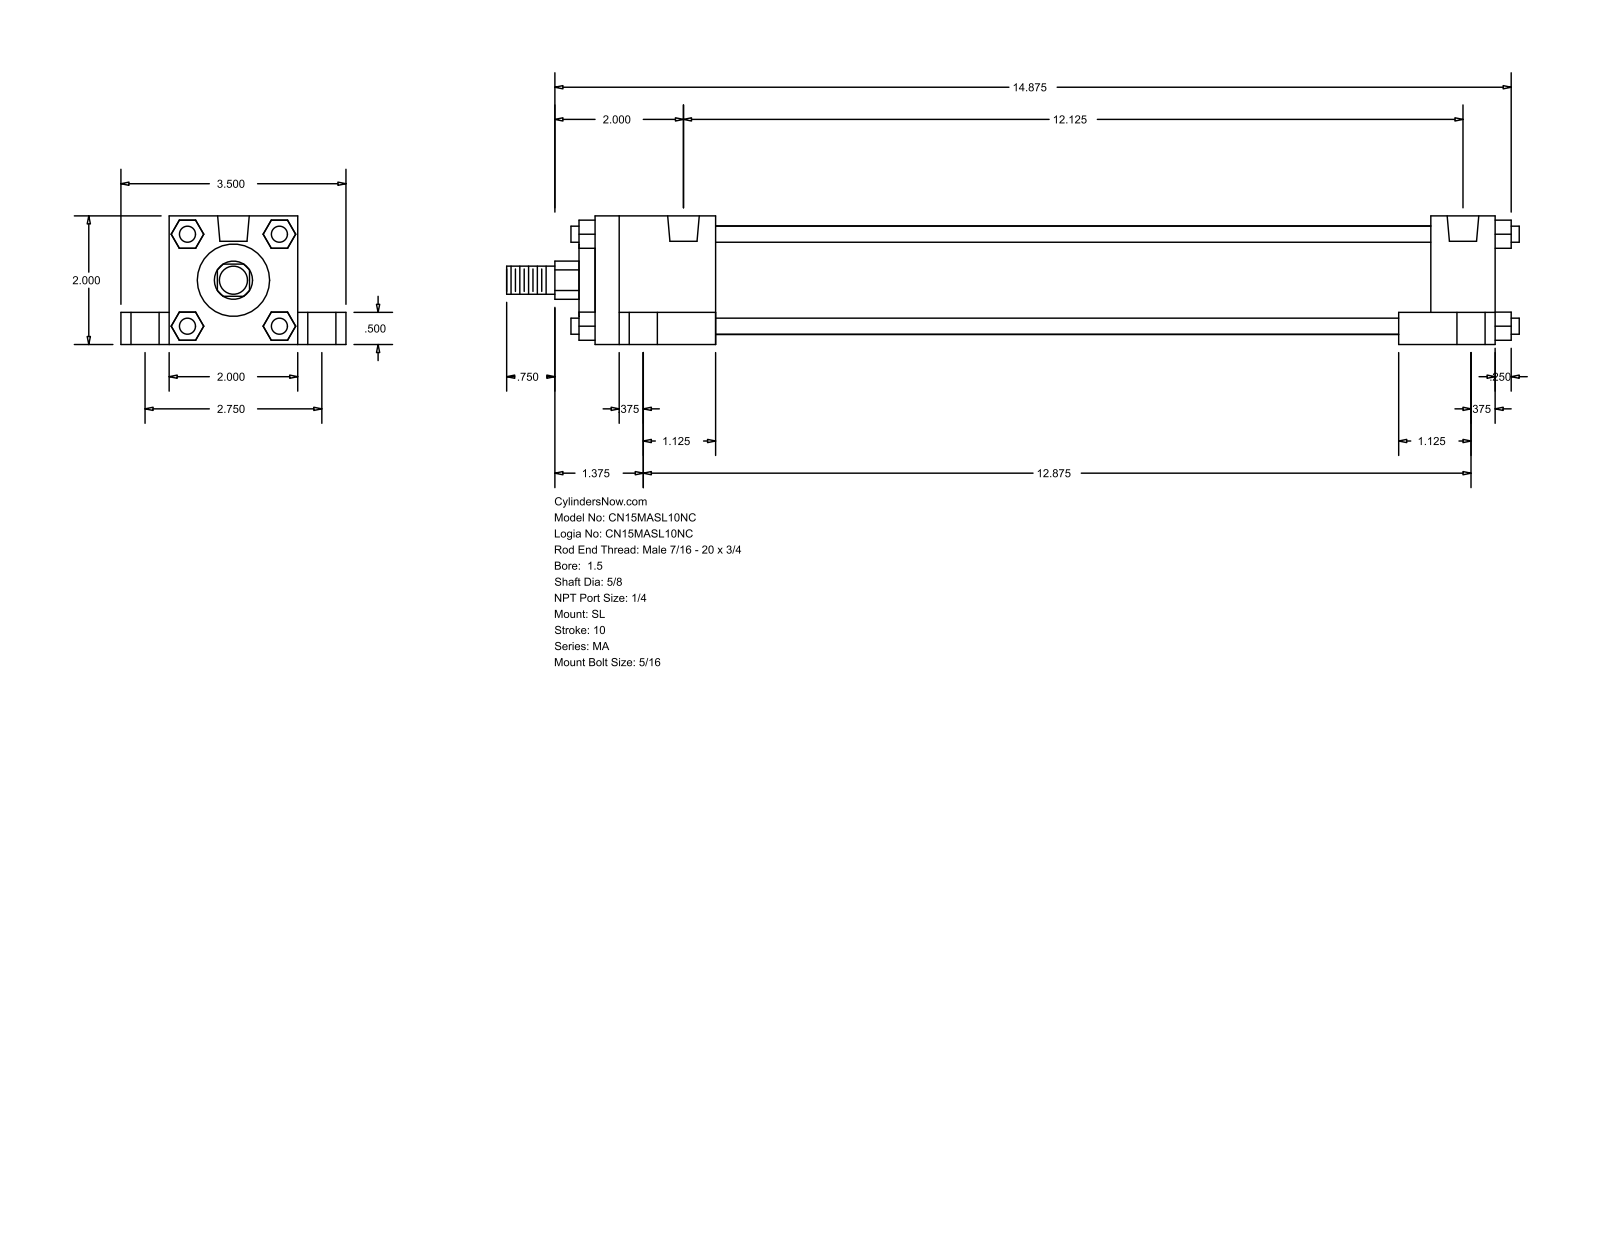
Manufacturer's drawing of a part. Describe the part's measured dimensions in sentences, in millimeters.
The part is named "MA_SL__0150_0.625". Its 3-D file was written by "GSSL Pune (CONFIG_CONTROL_DESIGN)". It is 0 solids with 148 faces: 112 planar, 36 cylindrical and 0 other. Overall it measures 400.05 by 88.9 by 50.8 millimeters. Round holes: 4 of diameter 7.94, 4 of diameter 11.11, 4 of diameter 17.46, 2 of diameter 12.49. Round bosses or shafts: 4 of diameter 6.35, 1 of diameter 42.93, 1 of diameter 28.57, 1 of diameter 15.88, 1 of diameter 11.11. Partial cylindrical surfaces (rounded edges, fillets, slot ends): 1 of radius 7.54. The main face-to-face distances are 50.8, 19.05, 38.1, 355.6, 69.85, 12.7, 282.57, 9.52, 330.19, 25.41. The hole center spacings are 35.06, 38.36, 69.84, 307.97, 313.1, 325.73, 327.03, 334.4.
